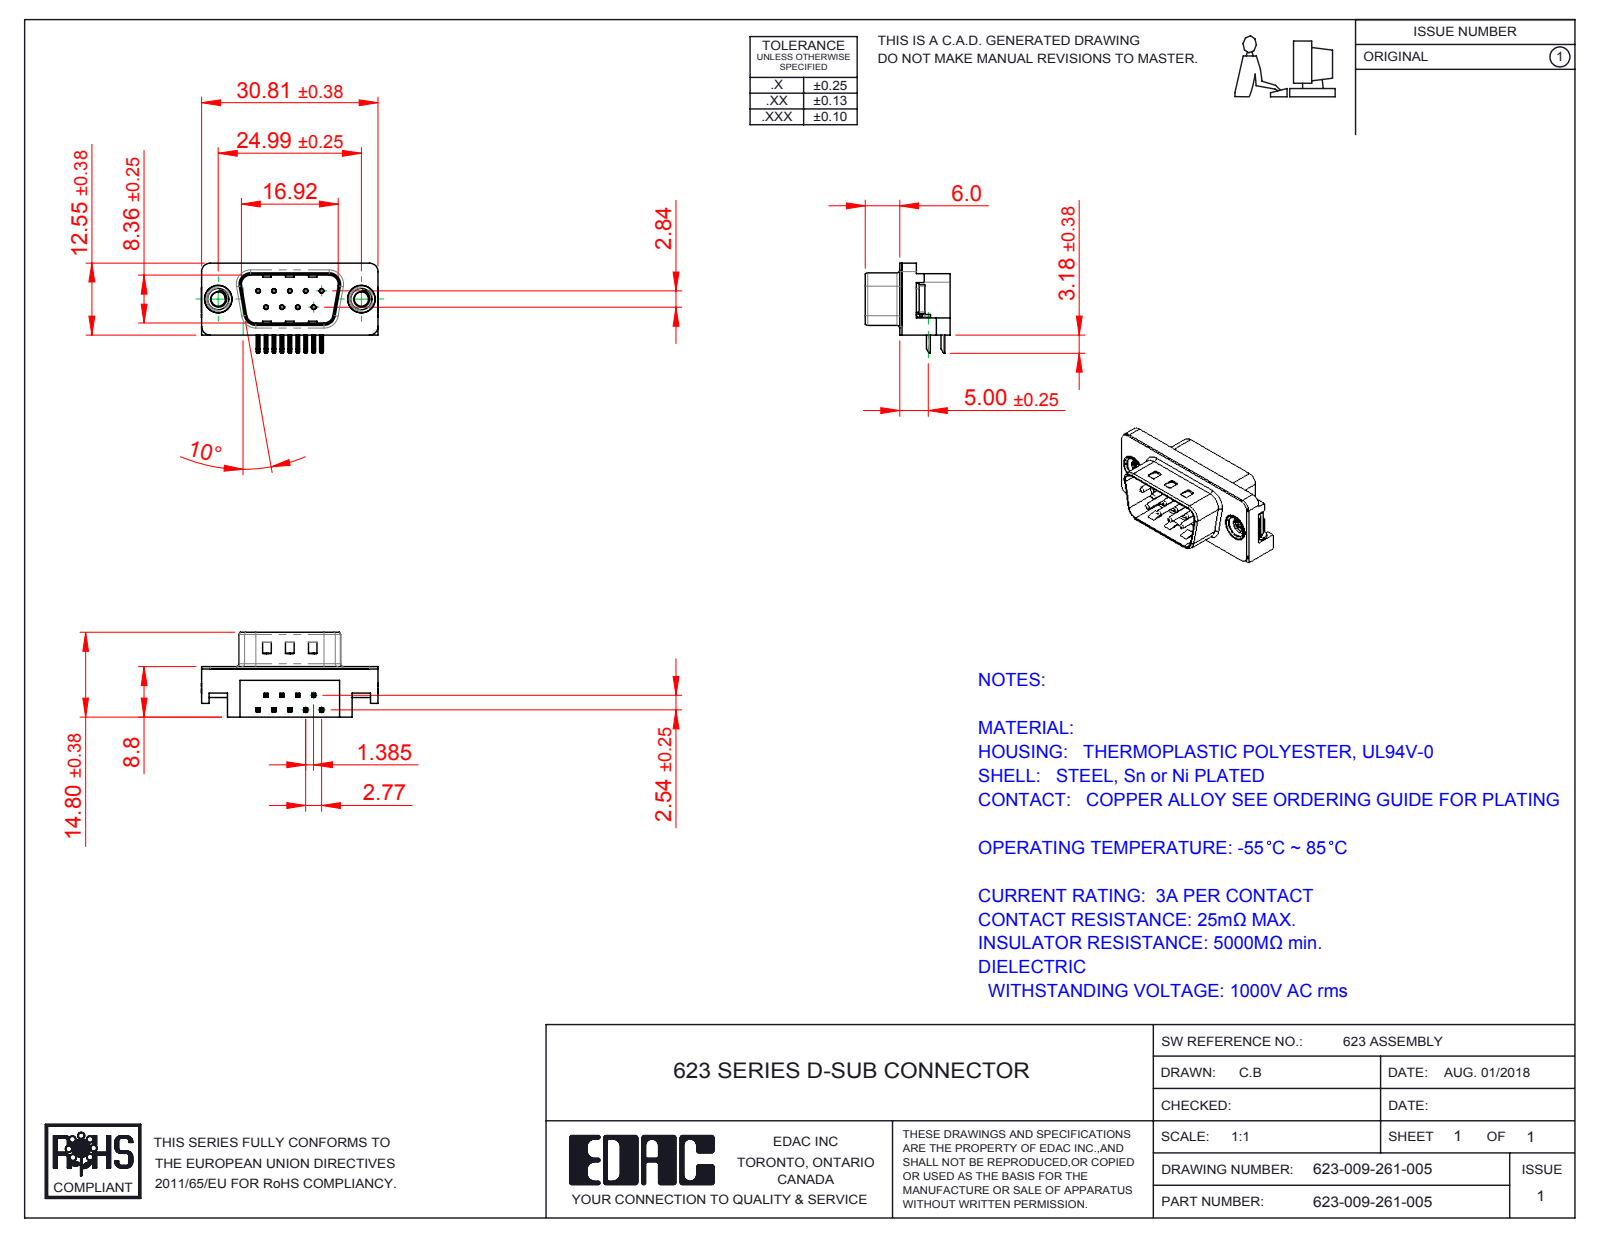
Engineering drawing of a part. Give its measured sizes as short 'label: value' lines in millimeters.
name: 623 M3 Threaded Rivet; 623 Contact Bottom; 623 Shell_9 Socket; 623 Non Board Mount (+3 more)
written by: SolidWorks 2016 (CONFIG_CONTROL_DESIGN)
unit: mm
bodies: 15 solids, 981 faces (573 planar, 309 cylindrical, 99 other)
size: 30.89 × 15.73 × 14.8
volume: 2 462 mm³; area: 3 779 mm²
holes: 9× ⌀0.35, 9× ⌀0.8, 2× ⌀2.5, 2× ⌀4, 2× ⌀4.8, 2× ⌀5
bosses: 9× ⌀0.75, 2× ⌀4.9, 2× ⌀4.75, 2× ⌀3.9
rounds: 44× R0.25, 18× R0.12, 16× R1, 9× R0.5, 8× R1.5, 4× R0.9, 4× R1.6, 4× R2
face distances: 0.4, 8.4, 8.8, 5.9, 2.9, 2.5, 0.35, 8.76, 10.69, 10.34
hole spacings: 3.16, 2.77, 5.54, 5.03, 5.04, 8.31, 7.48, 7.49
